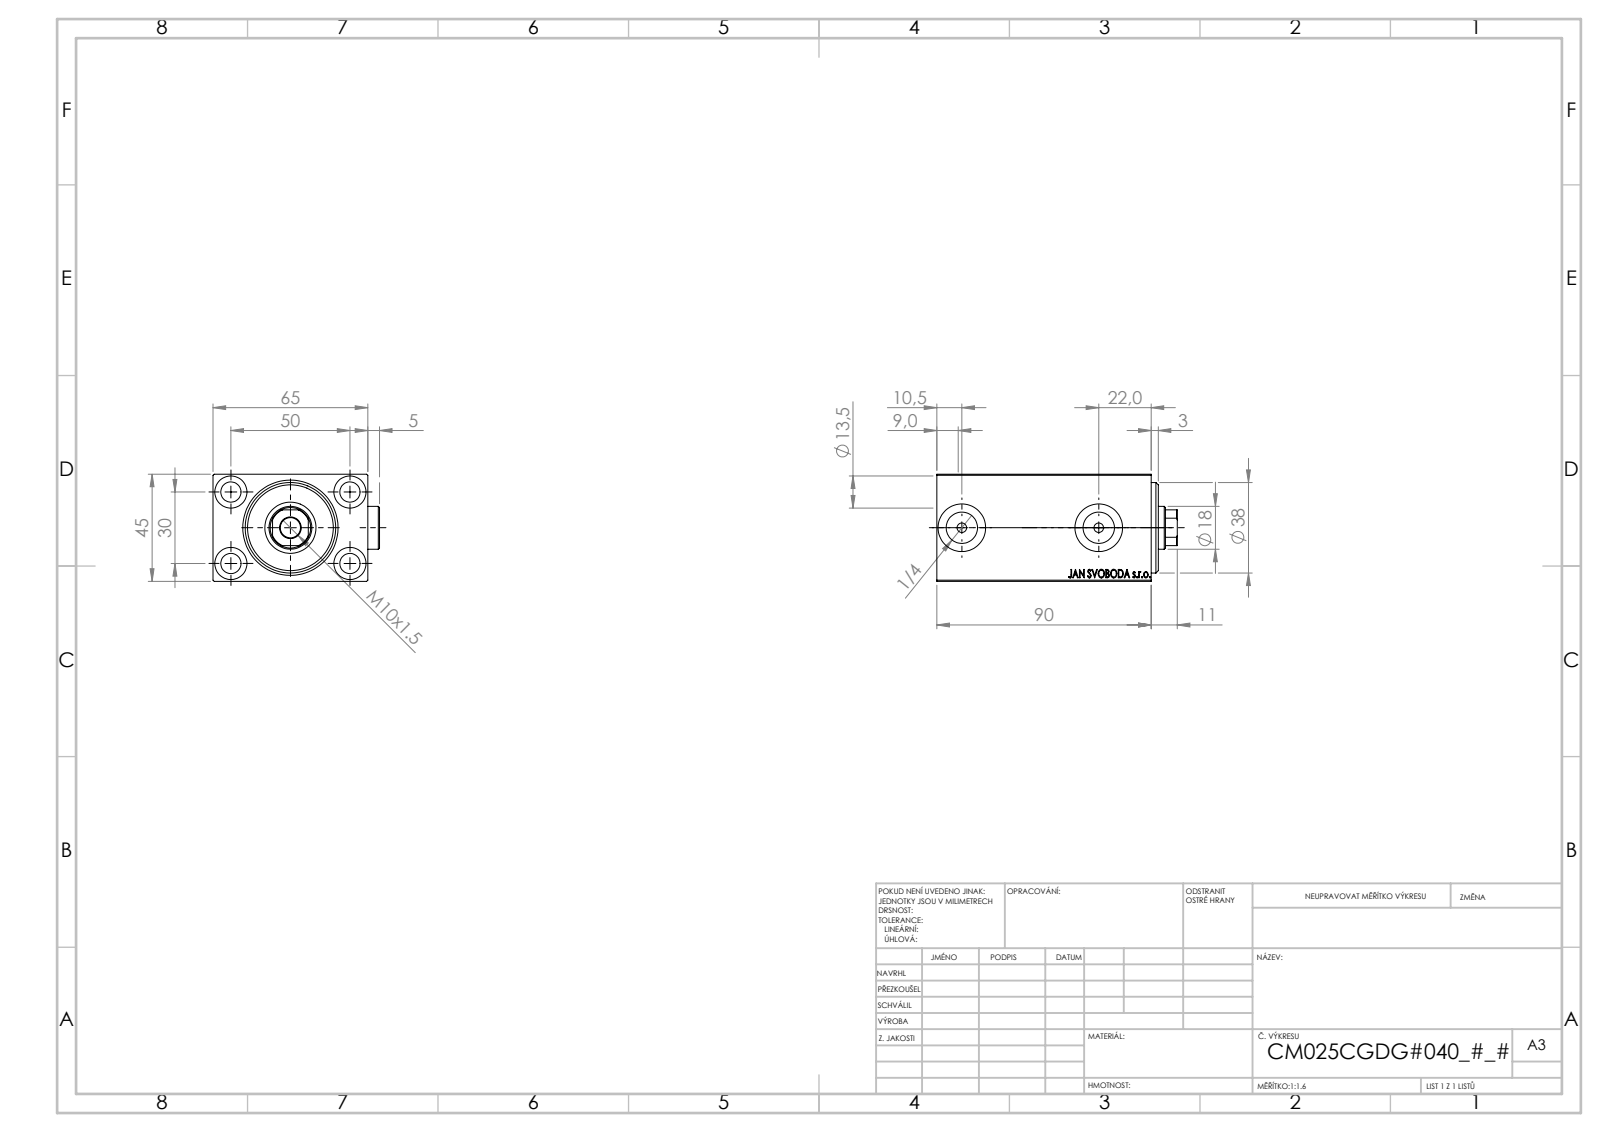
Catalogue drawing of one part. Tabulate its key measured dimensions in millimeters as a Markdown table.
| quantity | value |
| --- | --- |
| part name | V450CM_C_Body; Zatka_OIL_PORT; V450CM_C_VCP; V450CM_VC_B |
| STEP written by | SolidWorks 2019 (CONFIG_CONTROL_DESIGN) |
| units | millimeters |
| bodies | 5 solids, 916 faces (442 planar, 76 cylindrical, 398 other) |
| overall size | 101 × 69.9 × 45 |
| volume | 225 856 mm³ |
| surface area | 58 249 mm² |
| round holes (diameter × count) | 8.5 × 5, 13.5 × 4, 4 × 2, 13.16 × 2, 20 × 2, 18 × 1, 21.5 × 1, 25 × 1, 27 × 1, 38 × 1 |
| round bosses / shafts (diameter × count) | 18 × 2 |
| partial cylindrical surfaces (radius × count) | 8.5 × 1 |
| main face-to-face distances | 45, 65, 5, 6, 79, 84, 64.9, 85, 90, 3 |
| hole center spacings | 29.15, 30, 50, 58.31, 57.5 |
